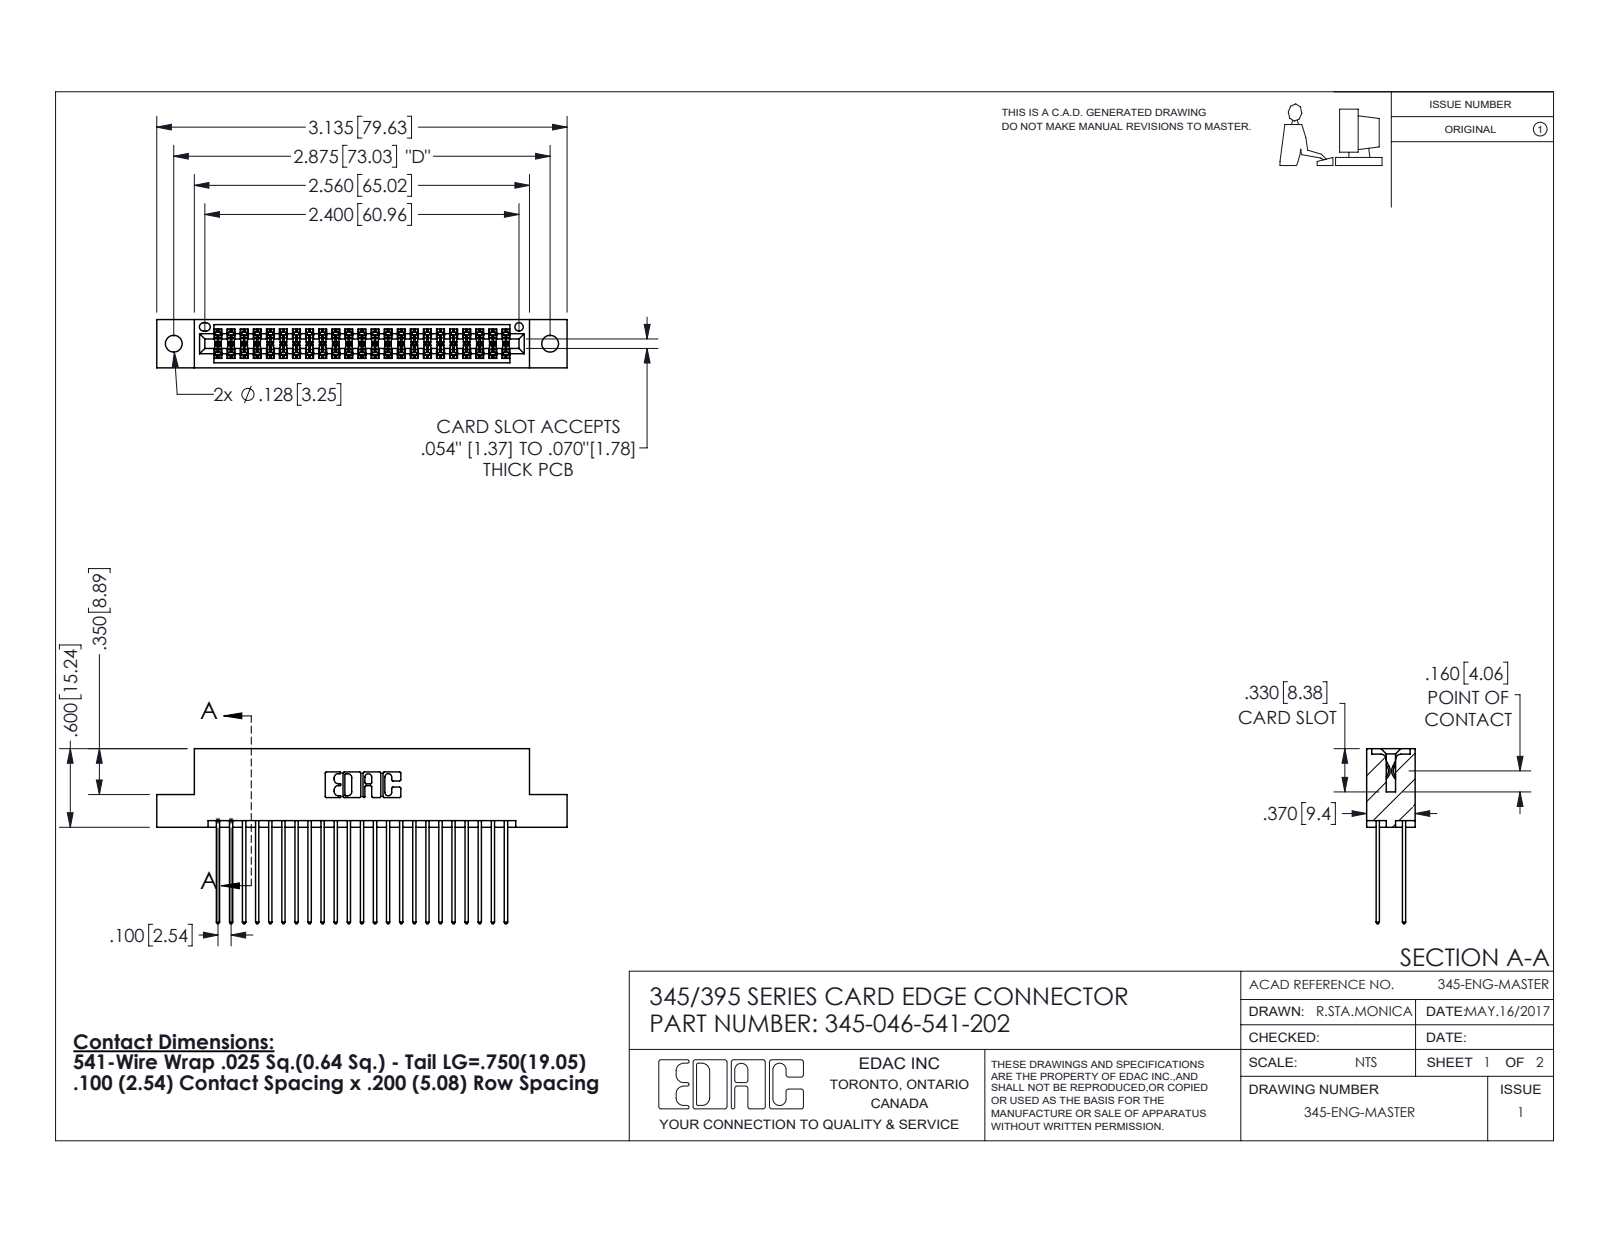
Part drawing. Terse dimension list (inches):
name: 345-292-001_345-293-141; 345-046-541-202; 345 Part_Flush Mounting Lugs - 0.128 Dia
written by: SolidWorks 2016 (CONFIG_CONTROL_DESIGN)
unit: in
bodies: 47 solids, 2426 faces (1598 planar, 828 cylindrical, 0 other)
size: 3.135 × 1.337 × 0.37
volume: 0.475 in³; area: 18.77 in²
holes: 2× ⌀0.128, 1× ⌀0.064
rounds: 69× R0.006, 46× R0.01, 22× R0.01, 6× R0.007, 6× R0.031, 3× R0.026, 2× R0.014, 2× R0.019
face distances: 0.298, 0.072, 0.2, 0.098, 0.272, 0.025, 0.37, 0.225, 0.175, 0.149
hole spacings: 0.27, 2.641, 2.875
